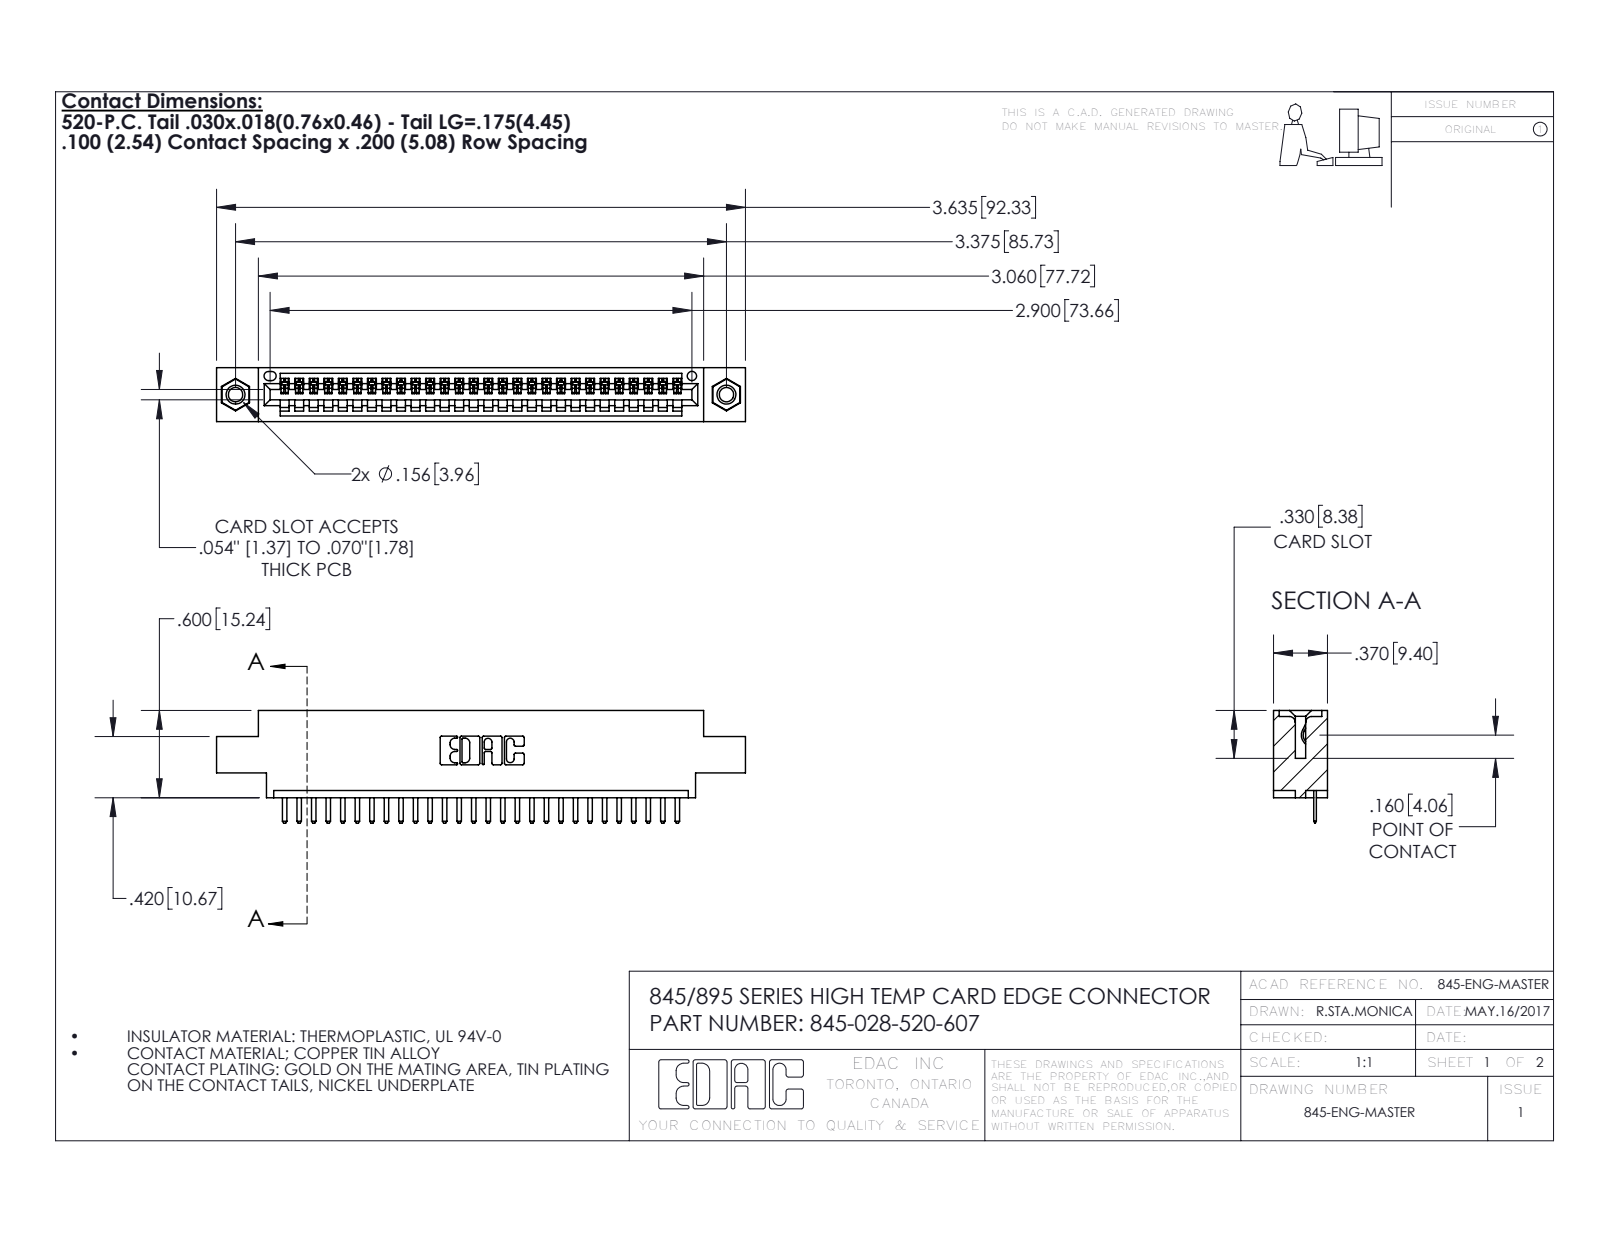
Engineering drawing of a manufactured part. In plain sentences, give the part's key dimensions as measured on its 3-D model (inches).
The part is named "345-292-001_345-293-120; 345-028-520-607; 345-250-001_345-250-005-103; 345 Part_0.170 Offset - 0.156 Dia-TI". Its 3-D file was written by "SolidWorks 2016 (CONFIG_CONTROL_DESIGN)". It is 31 solids with 1926 faces: 1292 planar, 618 cylindrical and 16 other. Overall it measures 3.635 by 0.775 by 0.37 inches. Its volume is 0.515 cubic inches and its surface area 16.94 square inches. Round holes: 2 of diameter 0.098, 2 of diameter 0.125, 2 of diameter 0.156, 1 of diameter 0.064. Round bosses or shafts: 2 of diameter 0.155. Partial cylindrical surfaces (rounded edges, fillets, slot ends): 58 of radius 0.01, 56 of radius 0.006, 22 of radius 0.01, 6 of radius 0.007, 6 of radius 0.031, 3 of radius 0.026, 2 of radius 0.031, 2 of radius 0.04. The main face-to-face distances are 0.072, 0.298, 0.37, 0.2, 0.098, 0.272, 0.025, 0.225, 0.072, 0.175. The hole center spacings are 0.27, 3.14, 3.375.
